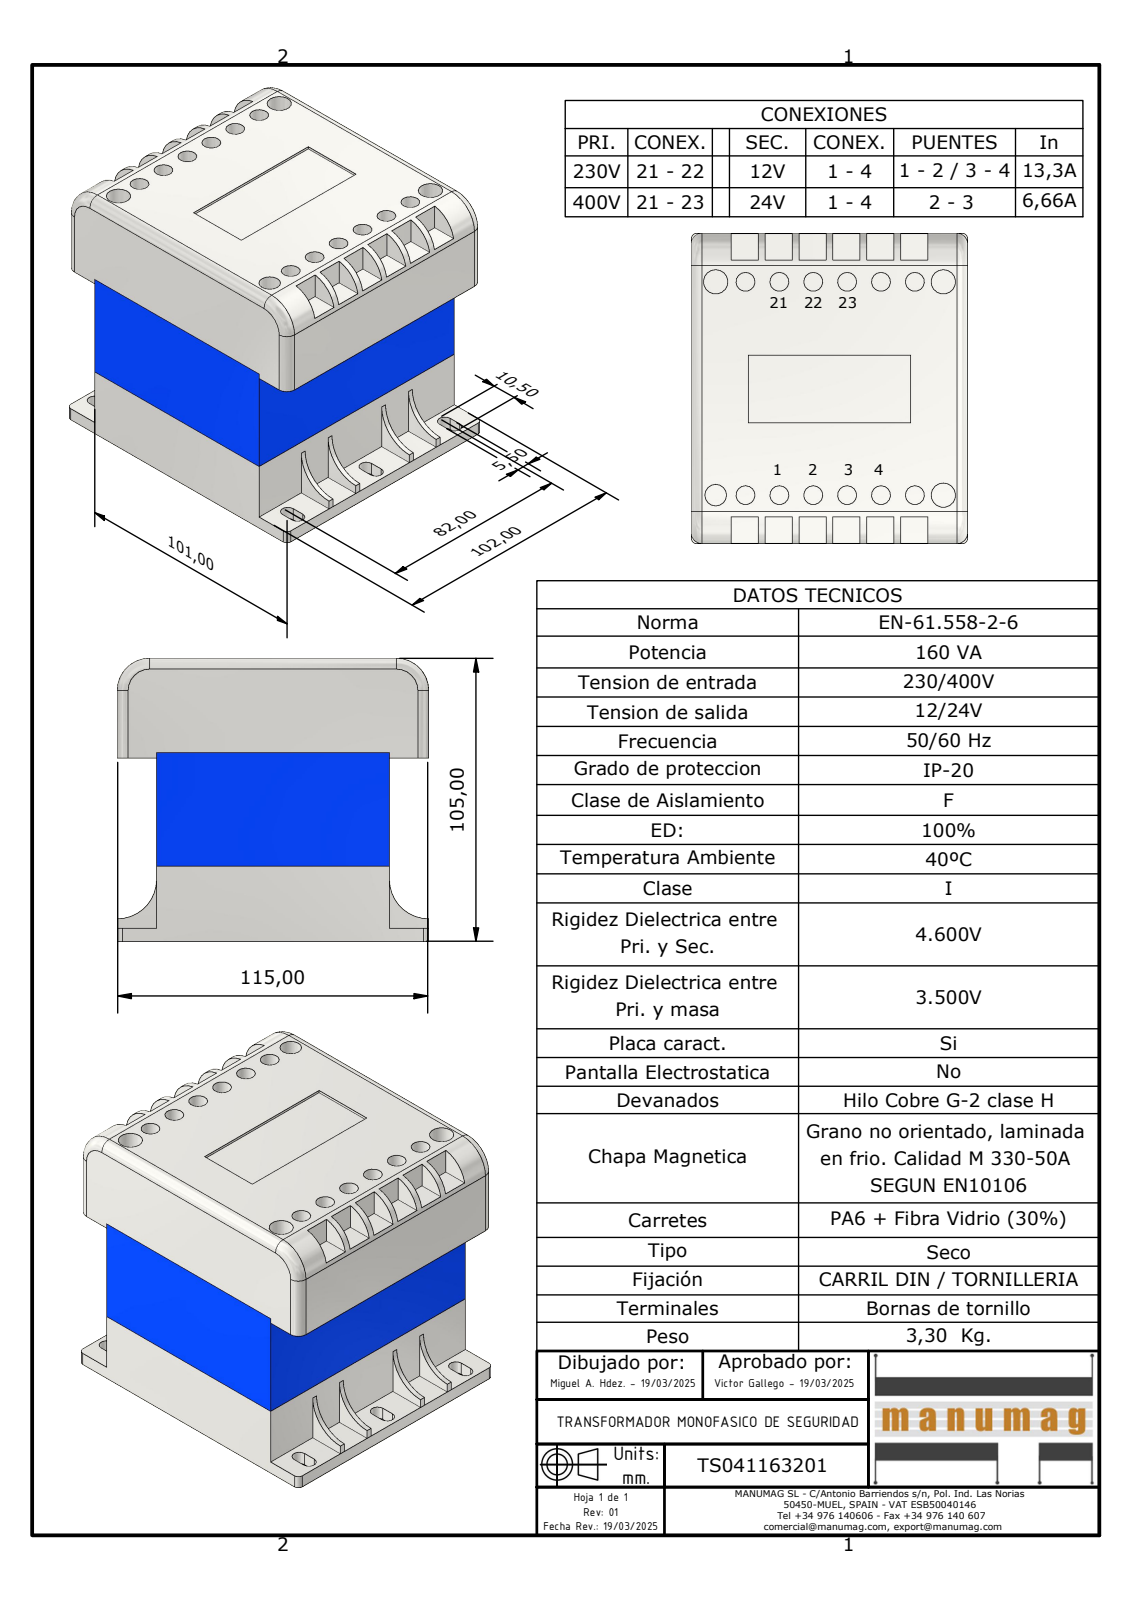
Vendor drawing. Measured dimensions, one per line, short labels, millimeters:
name: TS041163201; INFERIOR EI96; CENTRAL EI96-40; SUPERIOR EI96
written by: Autodesk Inventor 2023 (AUTOMOTIVE_DESIGN)
unit: mm
bodies: 11 solids, 200 faces (152 planar, 44 cylindrical, 4 other)
size: 115 × 105 × 102
volume: 475 560 mm³; area: 121 267 mm²
holes: 12× ⌀7, 3× ⌀9, 1× ⌀8
rounds: 8× R2.5, 6× R4, 4× R2, 2× R12, 2× R14.5
face distances: 1, 85, 100, 5, 101, 65, 102, 70, 105, 35
hole spacings: 12.5, 79.98, 25, 79, 82.86, 37.5, 87.45, 50
